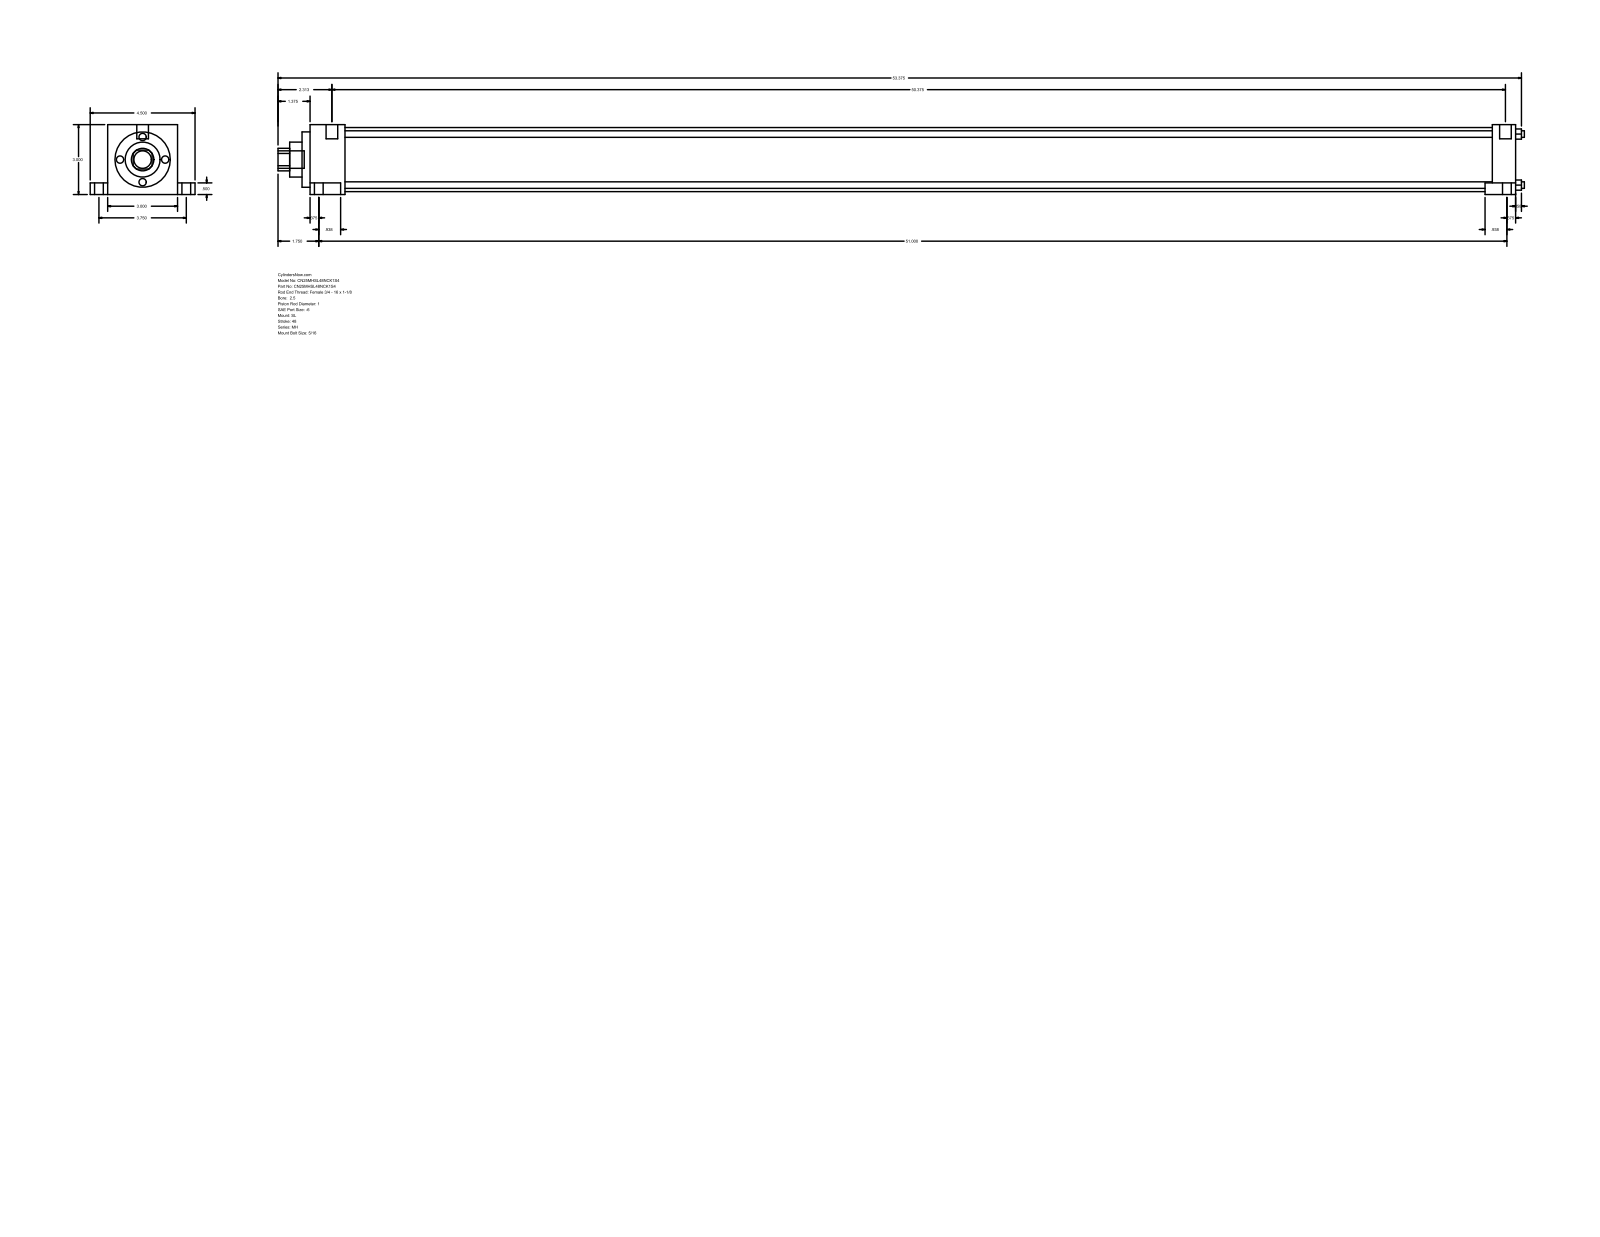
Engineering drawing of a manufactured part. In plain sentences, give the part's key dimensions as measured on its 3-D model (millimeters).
The part is named "MH_SL__0250_1". Its 3-D file was written by "GSSL Pune (CONFIG_CONTROL_DESIGN)". It is 0 solids with 86 faces: 61 planar, 25 cylindrical and 0 other. Overall it measures 1358.9 by 114.3 by 76.2 millimeters. Round holes: 4 of diameter 7.14, 1 of diameter 25.4, 1 of diameter 38.1, 1 of diameter 60.33, 1 of diameter 69.85. Round bosses or shafts: 2 of diameter 15.88, 2 of diameter 9.53, 2 of diameter 5.56, 1 of diameter 19.05, 1 of diameter 12.7. Partial cylindrical surfaces (rounded edges, fillets, slot ends): 1 of radius 12.29. The main face-to-face distances are 76.2, 25.41, 1297.78, 1323.19, 12.7, 63.5, 19.05, 95.25, 13.49, 1311.27. The hole center spacings are 39.33, 55.62, 78.66.
